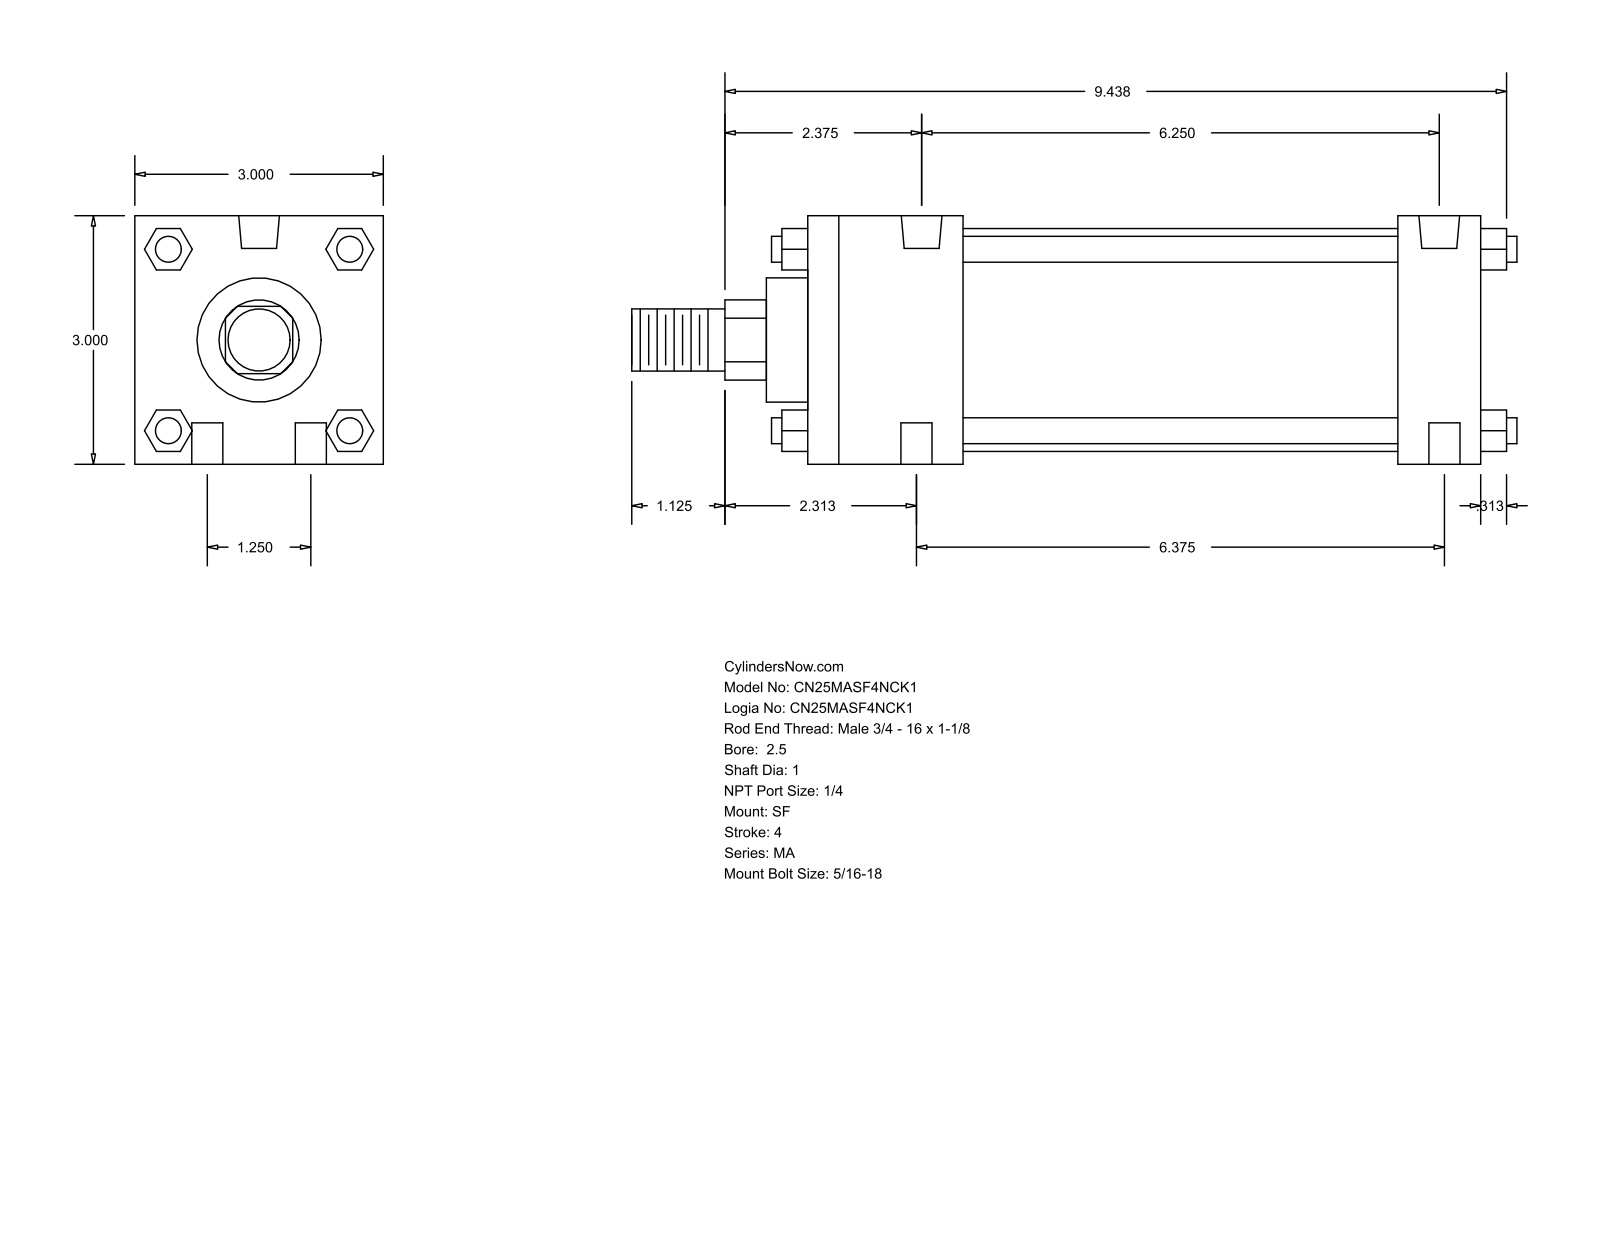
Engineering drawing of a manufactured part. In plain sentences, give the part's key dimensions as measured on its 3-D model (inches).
The part is named "MA_SF__0250_1". Its 3-D file was written by "GSSL Pune (CONFIG_CONTROL_DESIGN)". It is 0 solids with 124 faces: 94 planar, 30 cylindrical and 0 other. Overall it measures 10.687 by 3 by 3 inches. Round holes: 4 of diameter 0.375, 2 of diameter 0.313, 2 of diameter 0.492. Round bosses or shafts: 4 of diameter 0.313, 1 of diameter 2.69, 1 of diameter 1.5, 1 of diameter 1, 1 of diameter 0.75. Partial cylindrical surfaces (rounded edges, fillets, slot ends): 1 of radius 0.484. The main face-to-face distances are 3, 8.125, 0.5, 1, 7.125, 1.875, 5.25, 6.25, 1.095, 1.896. The hole center spacings are 0.628, 6.343, 1.25, 6.25, 6.375, 6.496.
